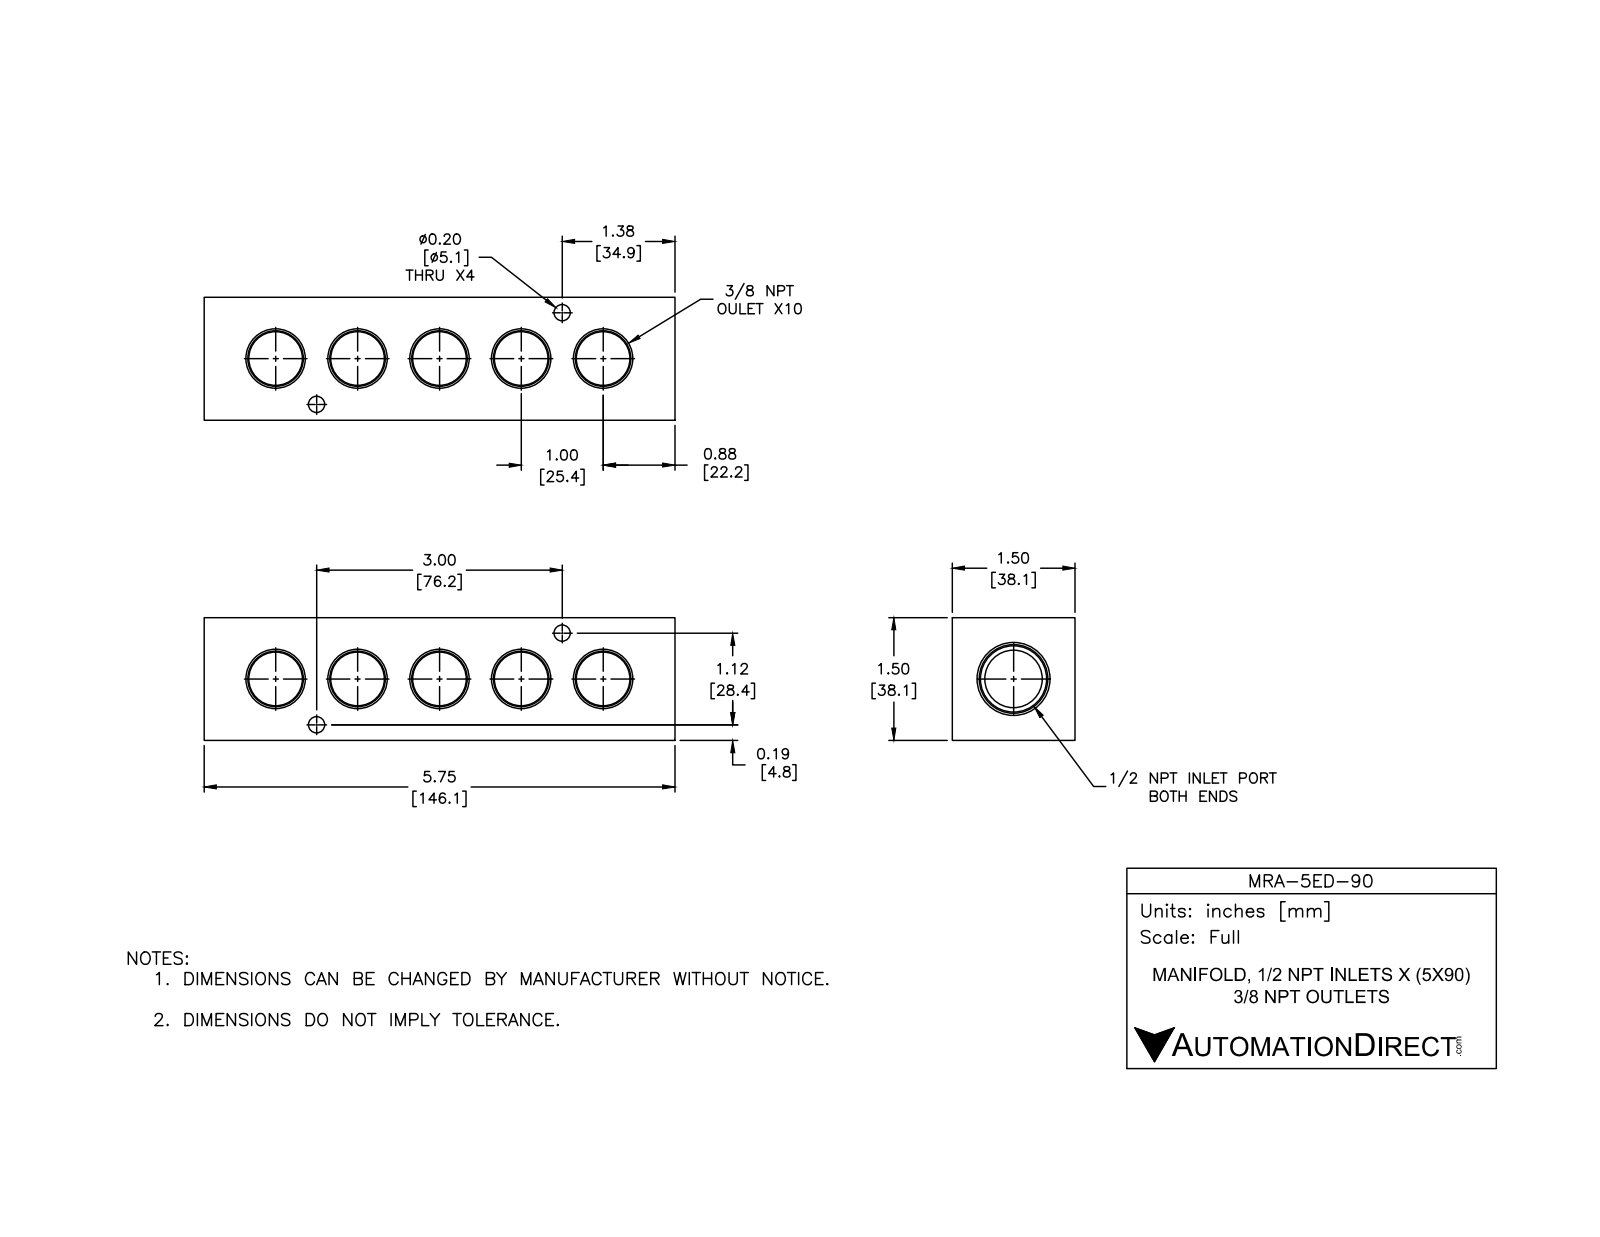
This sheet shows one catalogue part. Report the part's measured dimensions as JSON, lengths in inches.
{"part_name": "MRA-5ED-90", "step_written_by": "SolidWorks 2015 (CONFIG_CONTROL_DESIGN)", "units": "inches", "bodies": {"solids": 1, "faces": 114, "planar": 28, "cylindrical": 38, "other": 48}, "overall_size": [5.75, 1.5, 1.5], "volume_in3": 8.897, "surface_area_in2": 57.75, "round_holes": [[0.562, 10], [0.2, 4], [0.703, 1]], "face_to_face_distances": [1.5, 5.75, 1.09, 0.41, 0.53, 5.22, 4.69], "hole_center_spacings": [0.751, 1, 2, 1.601, 2.562, 3, 3.544, 3.202]}
